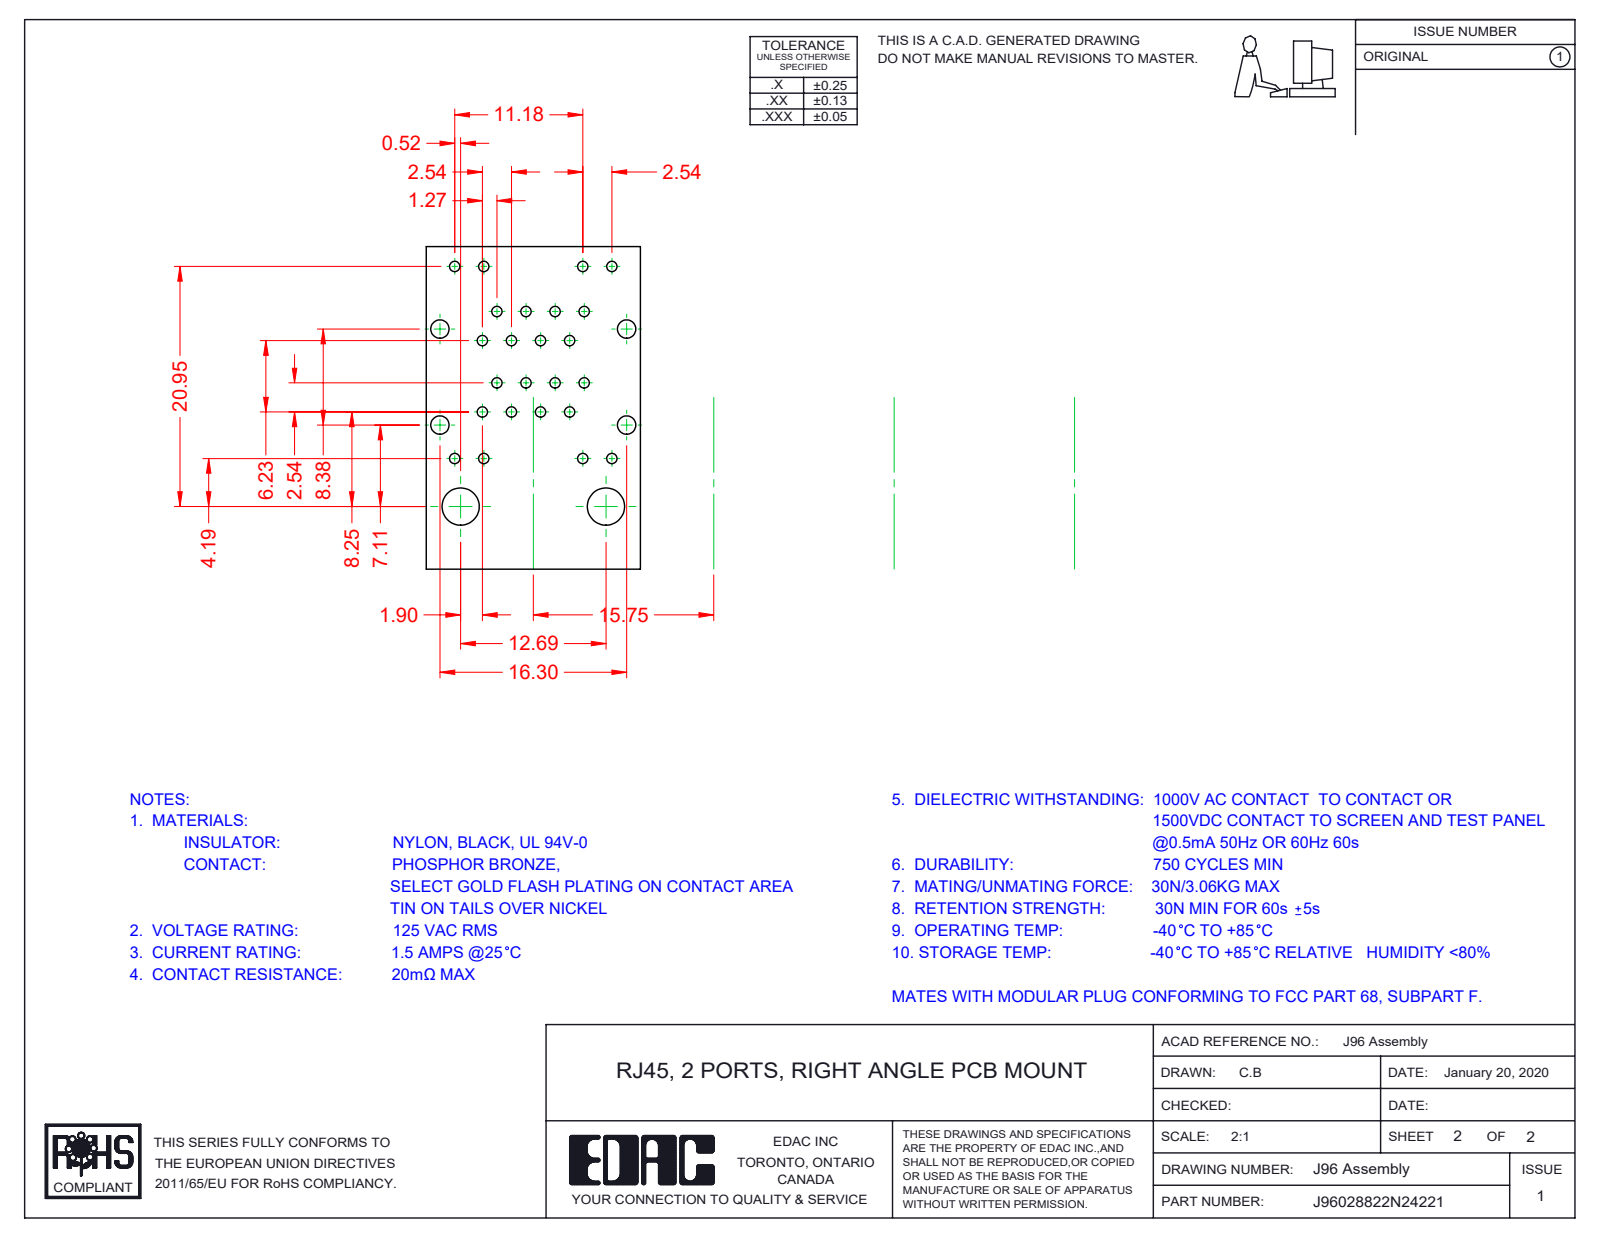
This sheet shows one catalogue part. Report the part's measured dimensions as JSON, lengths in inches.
{"part_name": "96 LED RH Lower_4-Orange; 96 Contacts Upper; J96028822N24221; 96 Contacts Lower (+8 more)", "step_written_by": "SolidWorks 2016 (CONFIG_CONTROL_DESIGN)", "units": "inches", "bodies": {"solids": 27, "faces": 2417, "planar": 1865, "cylindrical": 446, "other": 106}, "overall_size": [1.235, 1.129, 0.661], "volume_in3": 0.418, "surface_area_in2": 29.6, "partial_cylinders_radius": [[0.01, 48], [0.006, 32], [0.014, 24], [0.02, 16], [0.039, 16], [0.008, 14], [0.028, 9], [0.079, 5]], "face_to_face_distances": [0.642, 0.634, 0.069, 0.65, 0.581, 0.061, 0.573, 0.021, 0.058, 0.441]}
